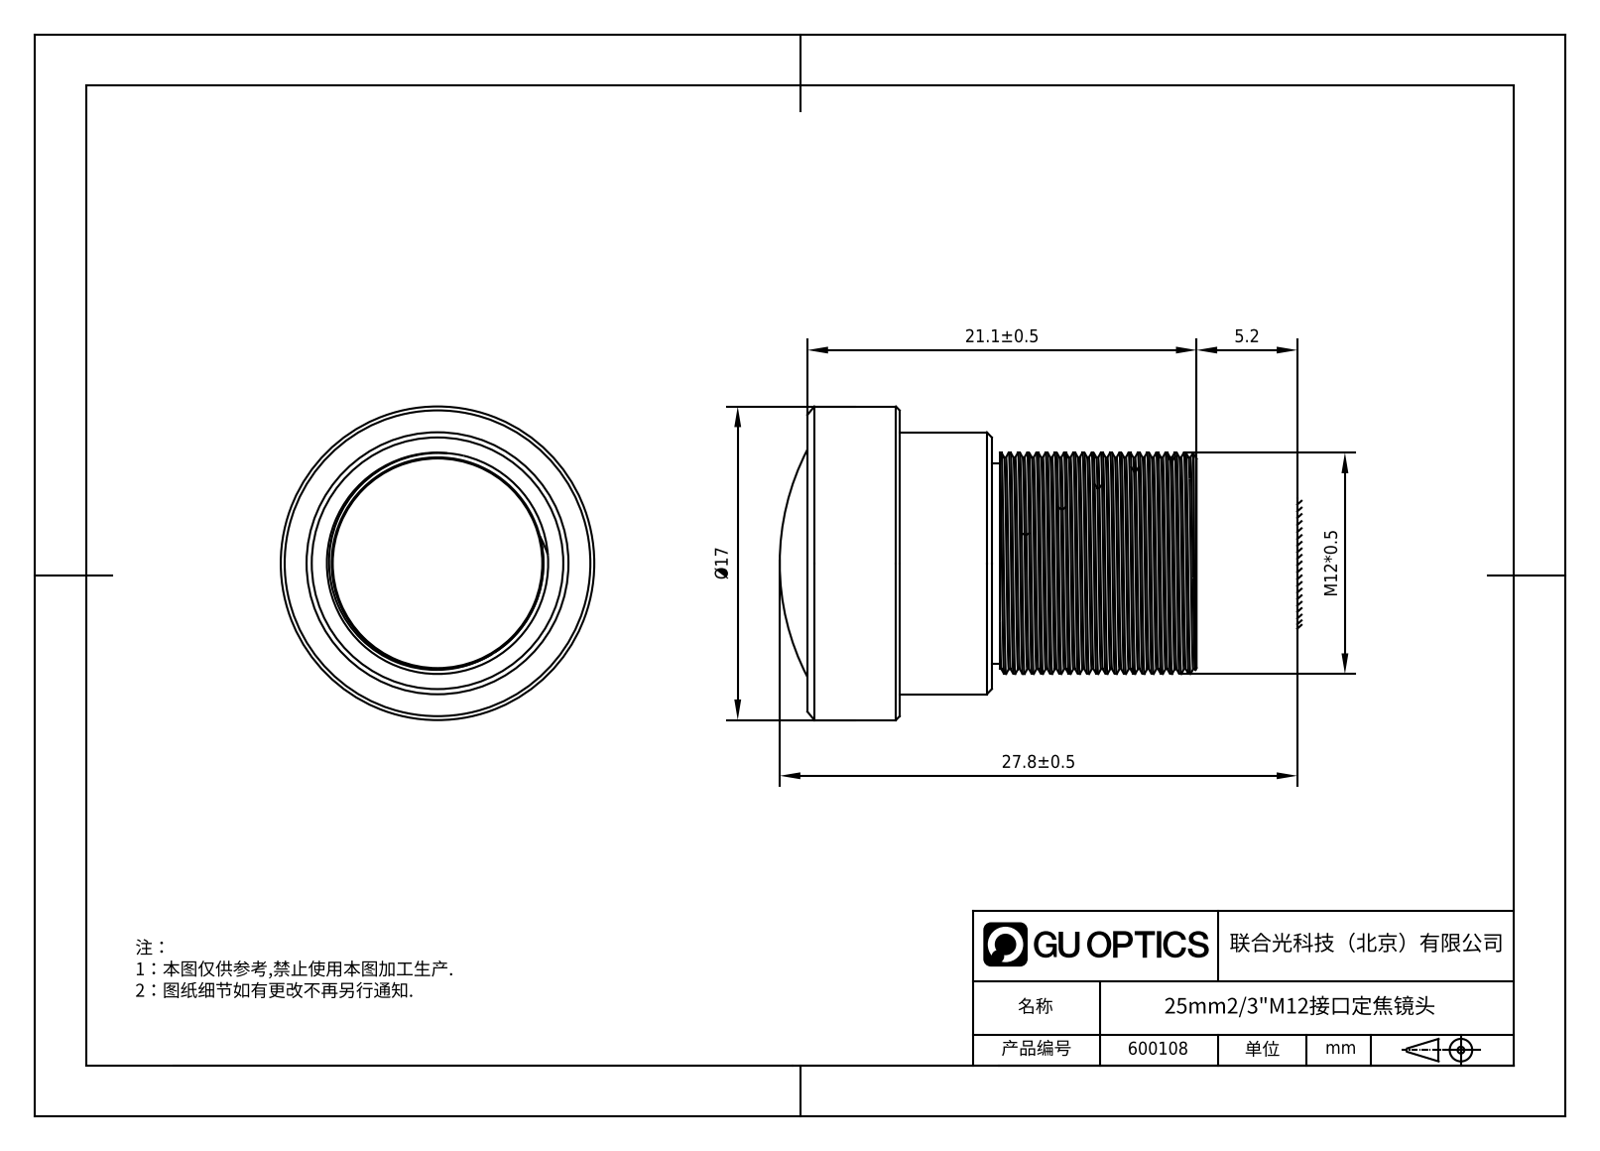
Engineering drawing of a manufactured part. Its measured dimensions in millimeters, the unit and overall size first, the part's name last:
Units: millimetres
Overall size (bounding box): 22.6 × 17 × 17
Round bosses / shafts (diameter × count): ⌀17 ×1, ⌀14.2 ×1, ⌀12 ×1, ⌀10.87 ×1
Main face-to-face distances: 5, 21.1, 16.1, 10, 11.1, 10.44, 5.44, 0.44, 10.66
Bodies: 0 solids, 35 faces (5 planar, 4 cylindrical, 26 other)
Part name (STEP PRODUCT): 600108
STEP written by: SolidWorks 2020 (CONFIG_CONTROL_DESIGN)
